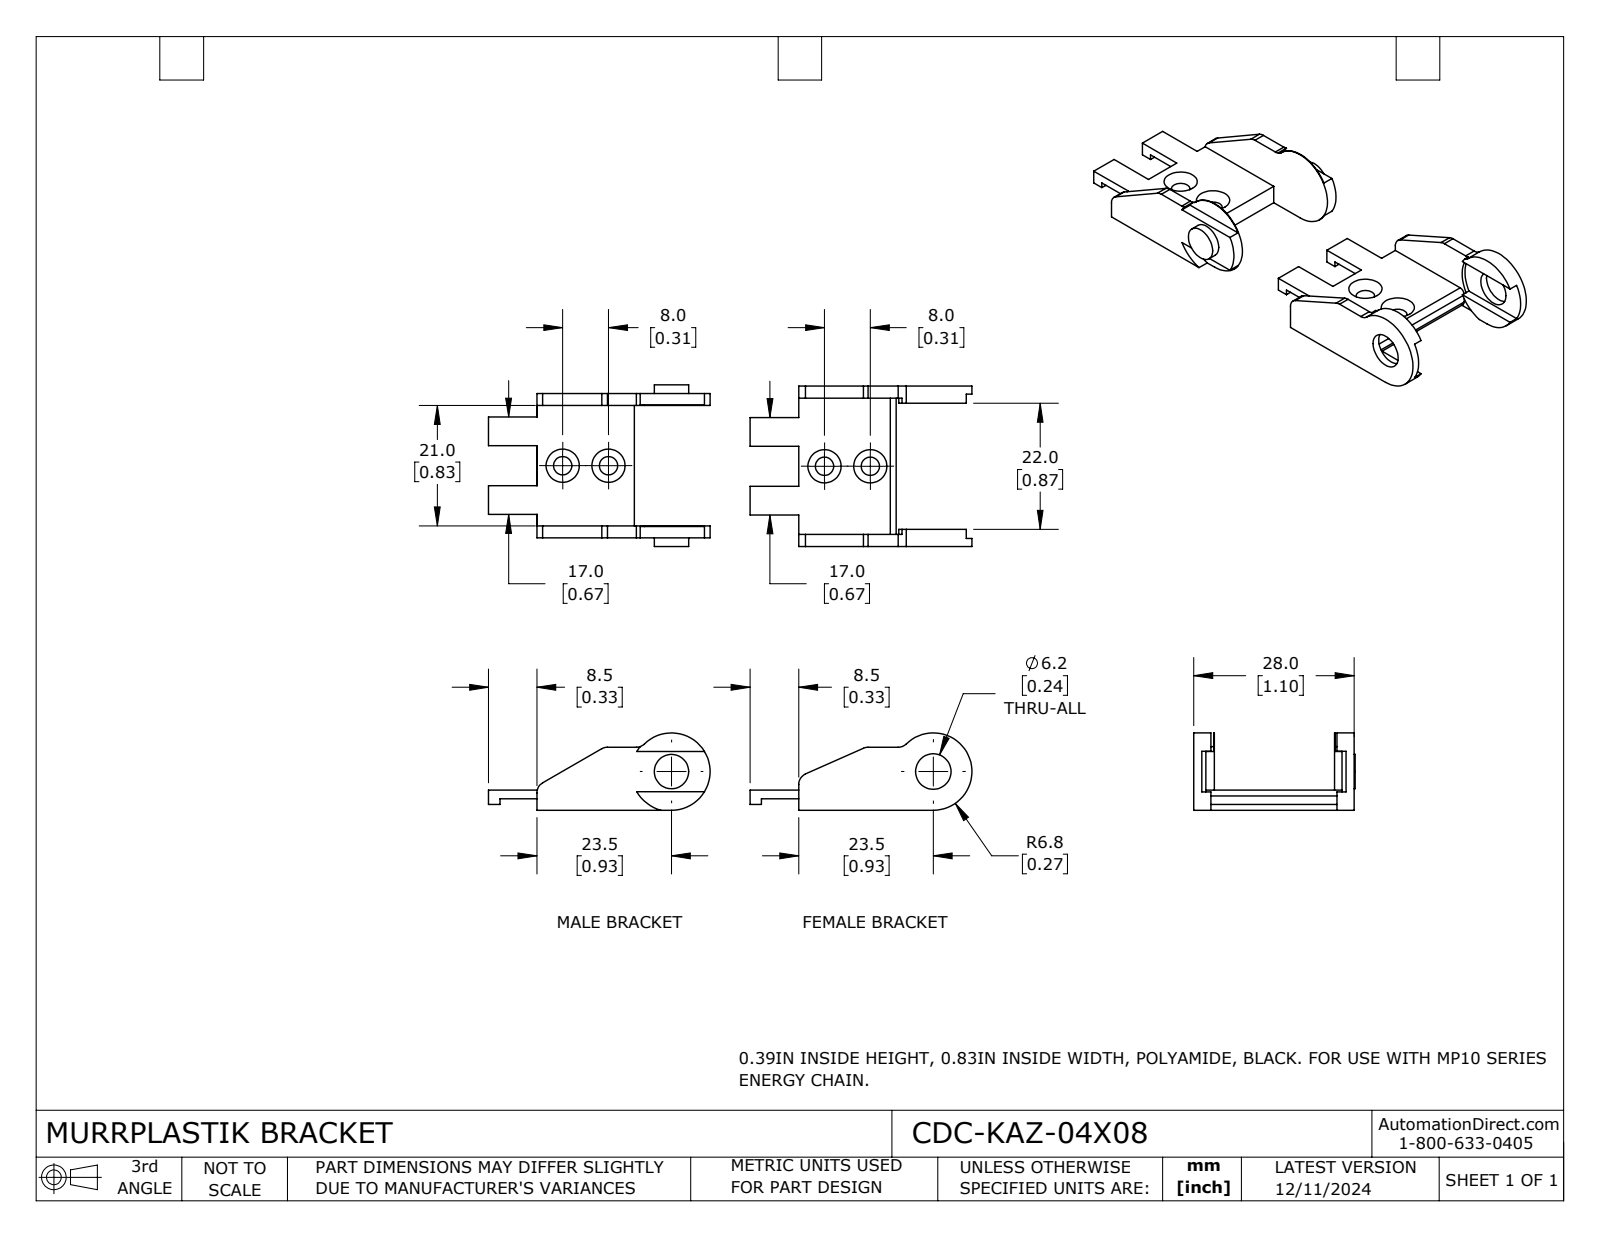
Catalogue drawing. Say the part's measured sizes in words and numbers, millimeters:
The part is named "CDC-KAZ-04X08". Its 3-D file was written by "SolidWorks 2024 (AUTOMOTIVE_DESIGN)". It is 2 solids with 109 faces: 68 planar, 37 cylindrical and 4 other. Overall it measures 84.4 by 28.2 by 13.5 millimeters. Its volume is 5 080 cubic millimeters and its surface area 5 340 square millimeters. Round holes: 4 of diameter 3.2, 1 of diameter 6.2. Round bosses or shafts: 1 of diameter 6. Partial cylindrical surfaces (rounded edges, fillets, slot ends): 6 of radius 2, 2 of radius 1, 2 of radius 6.8, 2 of radius 7. The main face-to-face distances are 3.5, 2.1, 1.5, 23.1, 24.6, 2, 24.4, 1.3, 25.2, 28. The hole center spacings are 8, 45.7, 37.7, 53.7.
